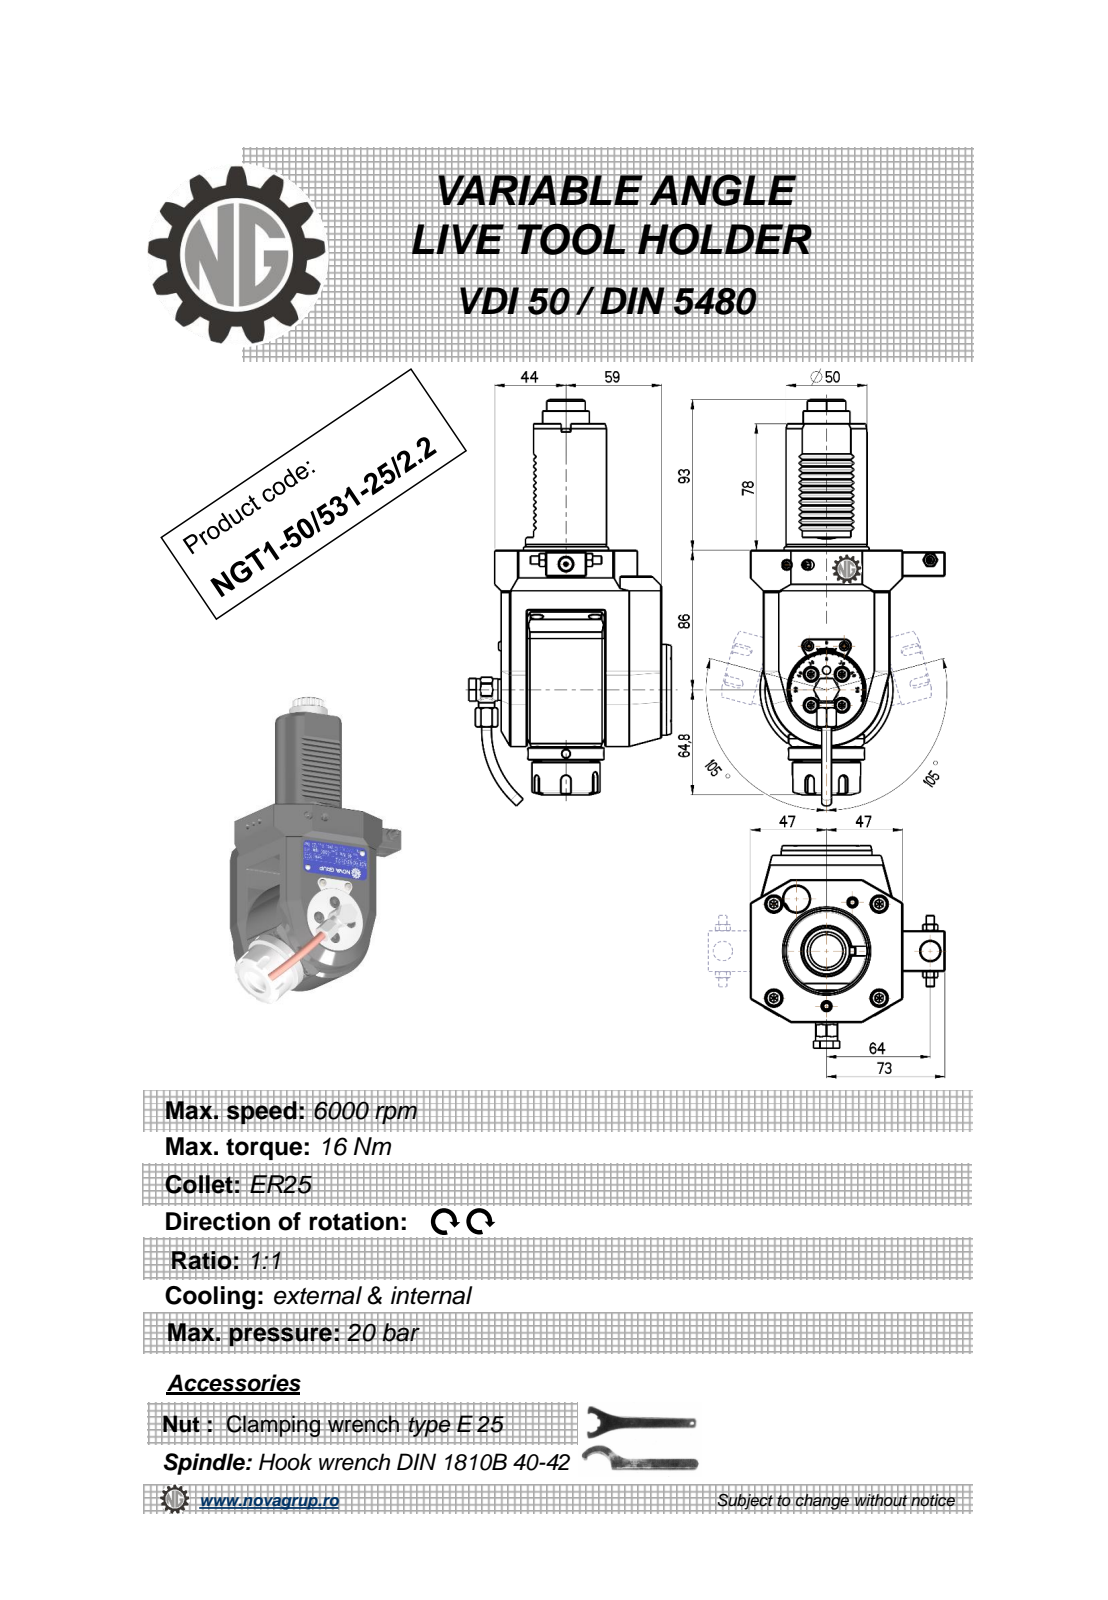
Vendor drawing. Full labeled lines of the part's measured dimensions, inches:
Part name (STEP PRODUCT): NGT1_50_531_25_2_2
STEP written by: PRO/ENGINEER BY PARAMETRIC TECHNOLOGY CORPORATION, 2010280 (CONFIG_CONTROL_DESIGN)
Units: inches
Bodies: 1 solid, 708 faces (271 planar, 211 cylindrical, 226 other)
Overall size (bounding box): 9.869 × 4.917 × 4.724
Volume: 63.59 in³ · Surface area: 141.4 in²
Round holes (diameter × count): ⌀0.157 ×3, ⌀0.197 ×2, ⌀0.118 ×1, ⌀0.165 ×1, ⌀0.244 ×1, ⌀0.354 ×1, ⌀0.374 ×1, ⌀0.394 ×1, ⌀0.433 ×1, ⌀0.472 ×1, ⌀0.799 ×1
Round bosses / shafts (diameter × count): ⌀0.236 ×2, ⌀0.224 ×2, ⌀2.205 ×1, ⌀1.969 ×1, ⌀1.85 ×1, ⌀1.654 ×1, ⌀1.378 ×1, ⌀1.134 ×1
Partial cylindrical surfaces — rounded edges, fillets, slot ends (radius × count): R0.12 ×36, R0.01 ×12, R0.012 ×12, R0.006 ×6, R0.118 ×5, R0.02 ×4, R0.039 ×2, R0.394 ×2
Main face-to-face distances: 1.457, 3.898, 3.071, 0.315, 0.63, 0.787, 0.236, 2.52, 4.134, 0.827
Hole centre spacings: 0.016, 1.553, 1.929, 1.945, 2.52, 3.173, 3.183, 4.033
